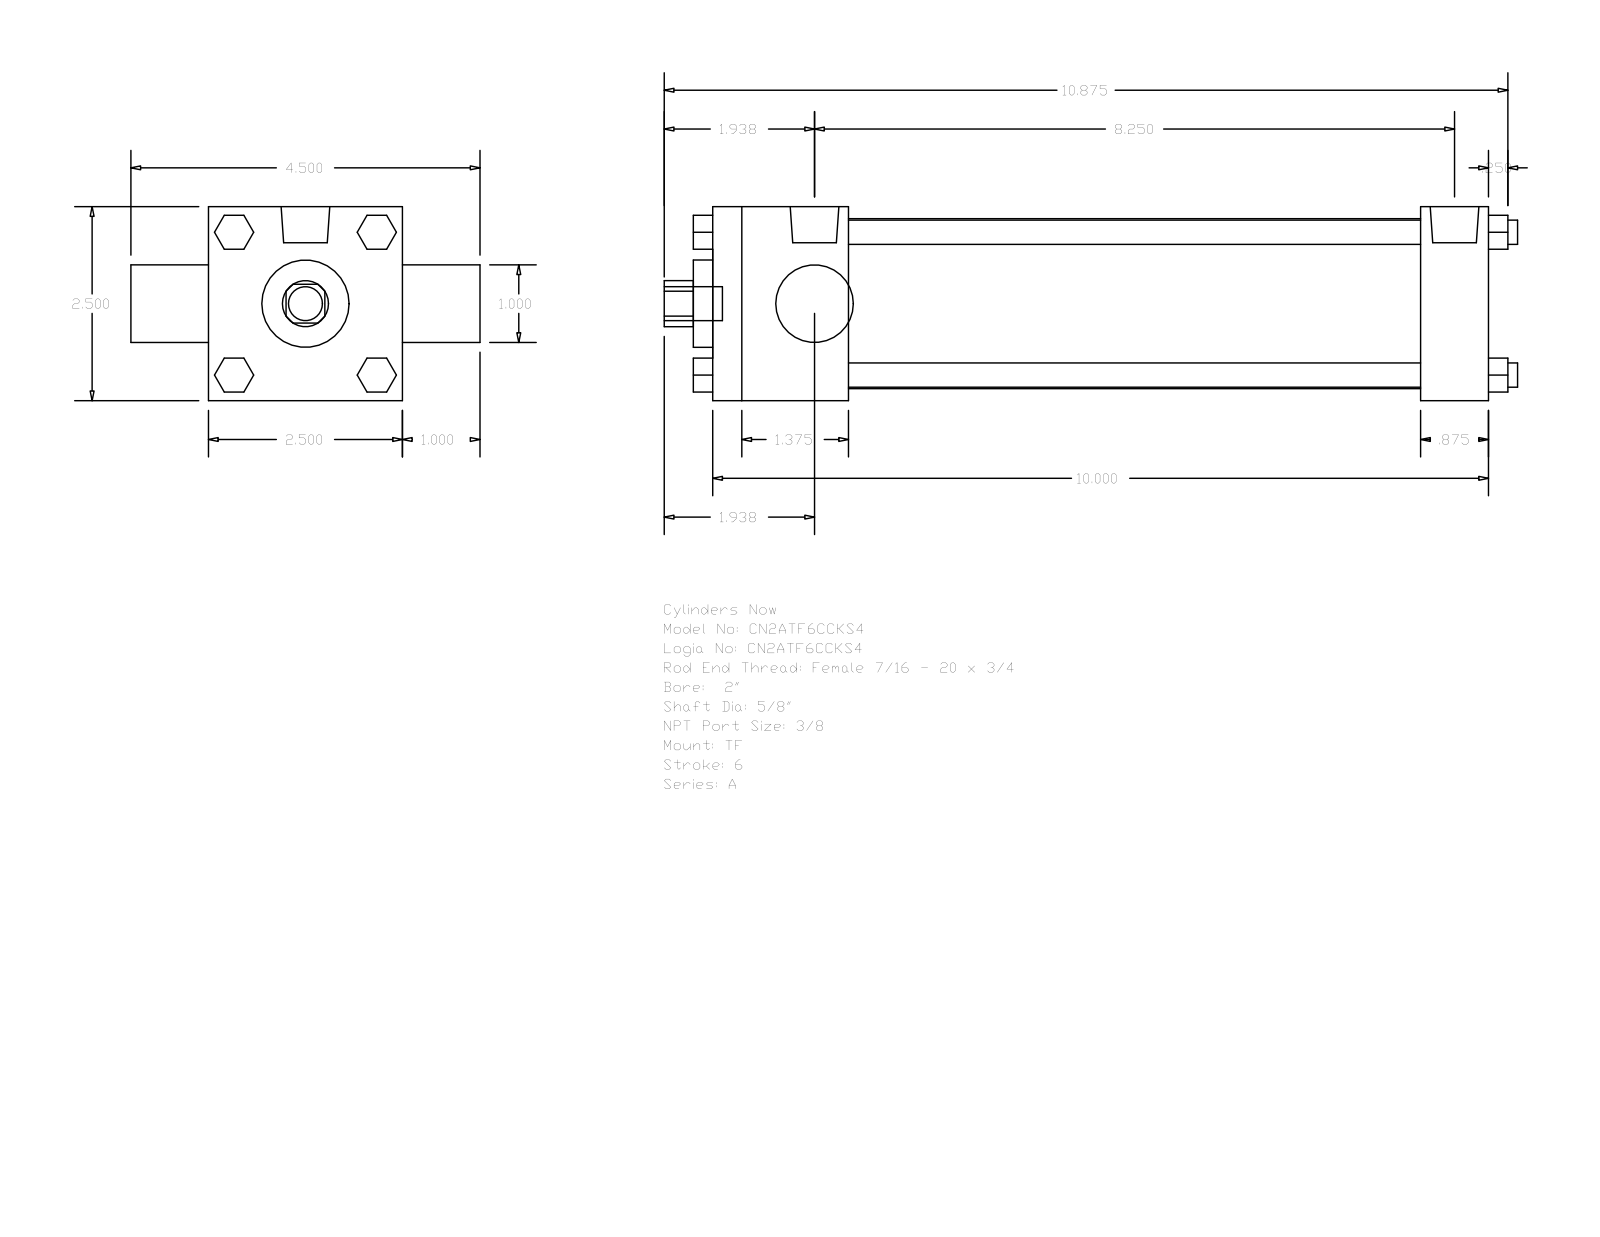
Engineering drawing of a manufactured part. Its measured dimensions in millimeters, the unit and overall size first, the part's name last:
Units: millimetres
Overall size (bounding box): 279.4 × 114.3 × 63.5
Round holes (diameter × count): ⌀15.88 ×1, ⌀25.4 ×1, ⌀28.57 ×1, ⌀55.63 ×1
Round bosses / shafts (diameter × count): ⌀7.94 ×4, ⌀5.56 ×3, ⌀15.93 ×2, ⌀11.11 ×1
Partial cylindrical surfaces — rounded edges, fillets, slot ends (radius × count): R7.54 ×1
Main face-to-face distances: 63.5, 254, 44.45, 231.77, 187.32, 209.55, 22.23, 25.4, 88.9, 260.35
Bodies: 0 solids, 120 faces (92 planar, 28 cylindrical, 0 other)
Part name (STEP PRODUCT): A_TF__0200_0.625
STEP written by: GSSL Pune (CONFIG_CONTROL_DESIGN)
